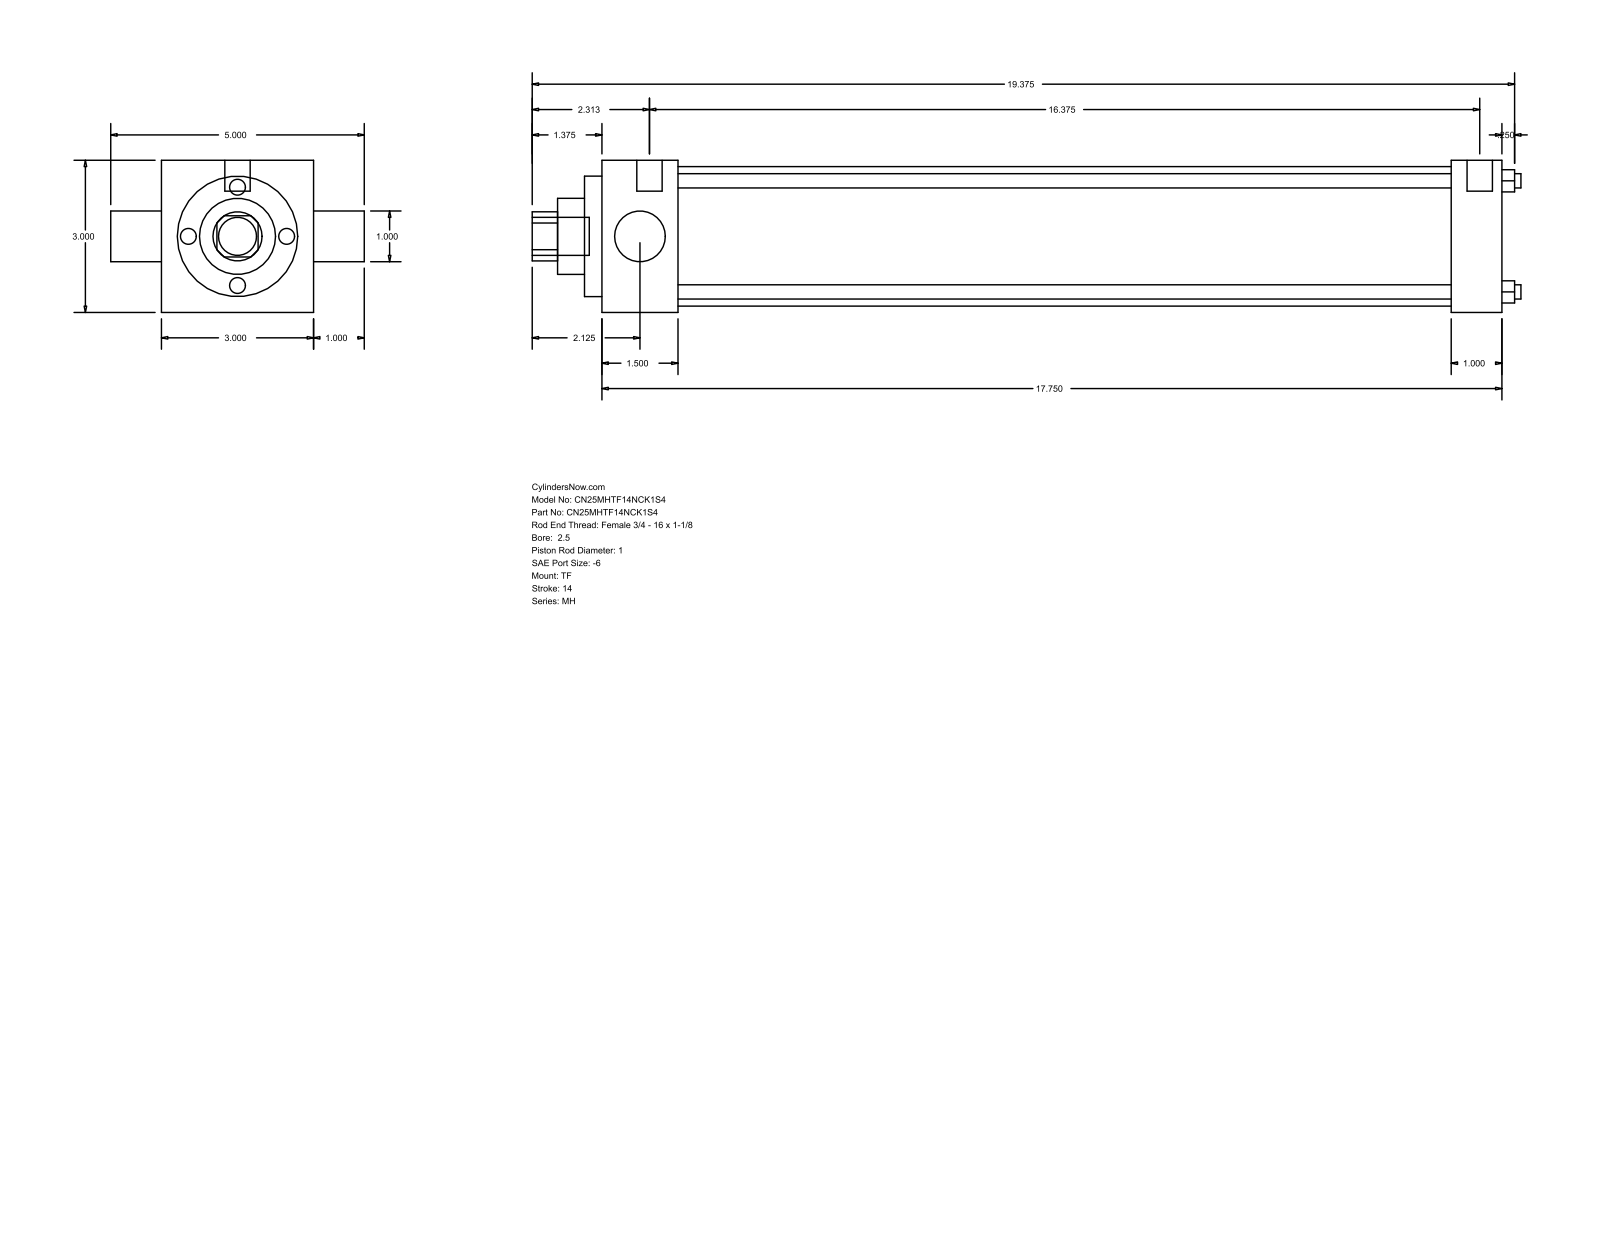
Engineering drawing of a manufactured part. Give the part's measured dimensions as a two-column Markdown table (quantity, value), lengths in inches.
| quantity | value |
| --- | --- |
| part name | MH_TF__0250_1 |
| STEP written by | GSSL Pune (CONFIG_CONTROL_DESIGN) |
| units | inches |
| bodies | 0 solids, 86 faces (61 planar, 25 cylindrical, 0 other) |
| overall size | 19.5 × 5 × 3 |
| round holes (diameter × count) | 0.281 × 4, 1 × 2, 1.5 × 1, 2.375 × 1, 2.75 × 1 |
| round bosses / shafts (diameter × count) | 0.219 × 3, 0.5 × 2, 0.75 × 1 |
| partial cylindrical surfaces (radius × count) | 0.484 × 1 |
| main face-to-face distances | 3, 17.75, 1, 1.5, 16.25, 16.75, 15.25, 0.344, 1.844, 17.094 |
| hole center spacings | 1.548, 2.19, 3.097 |
